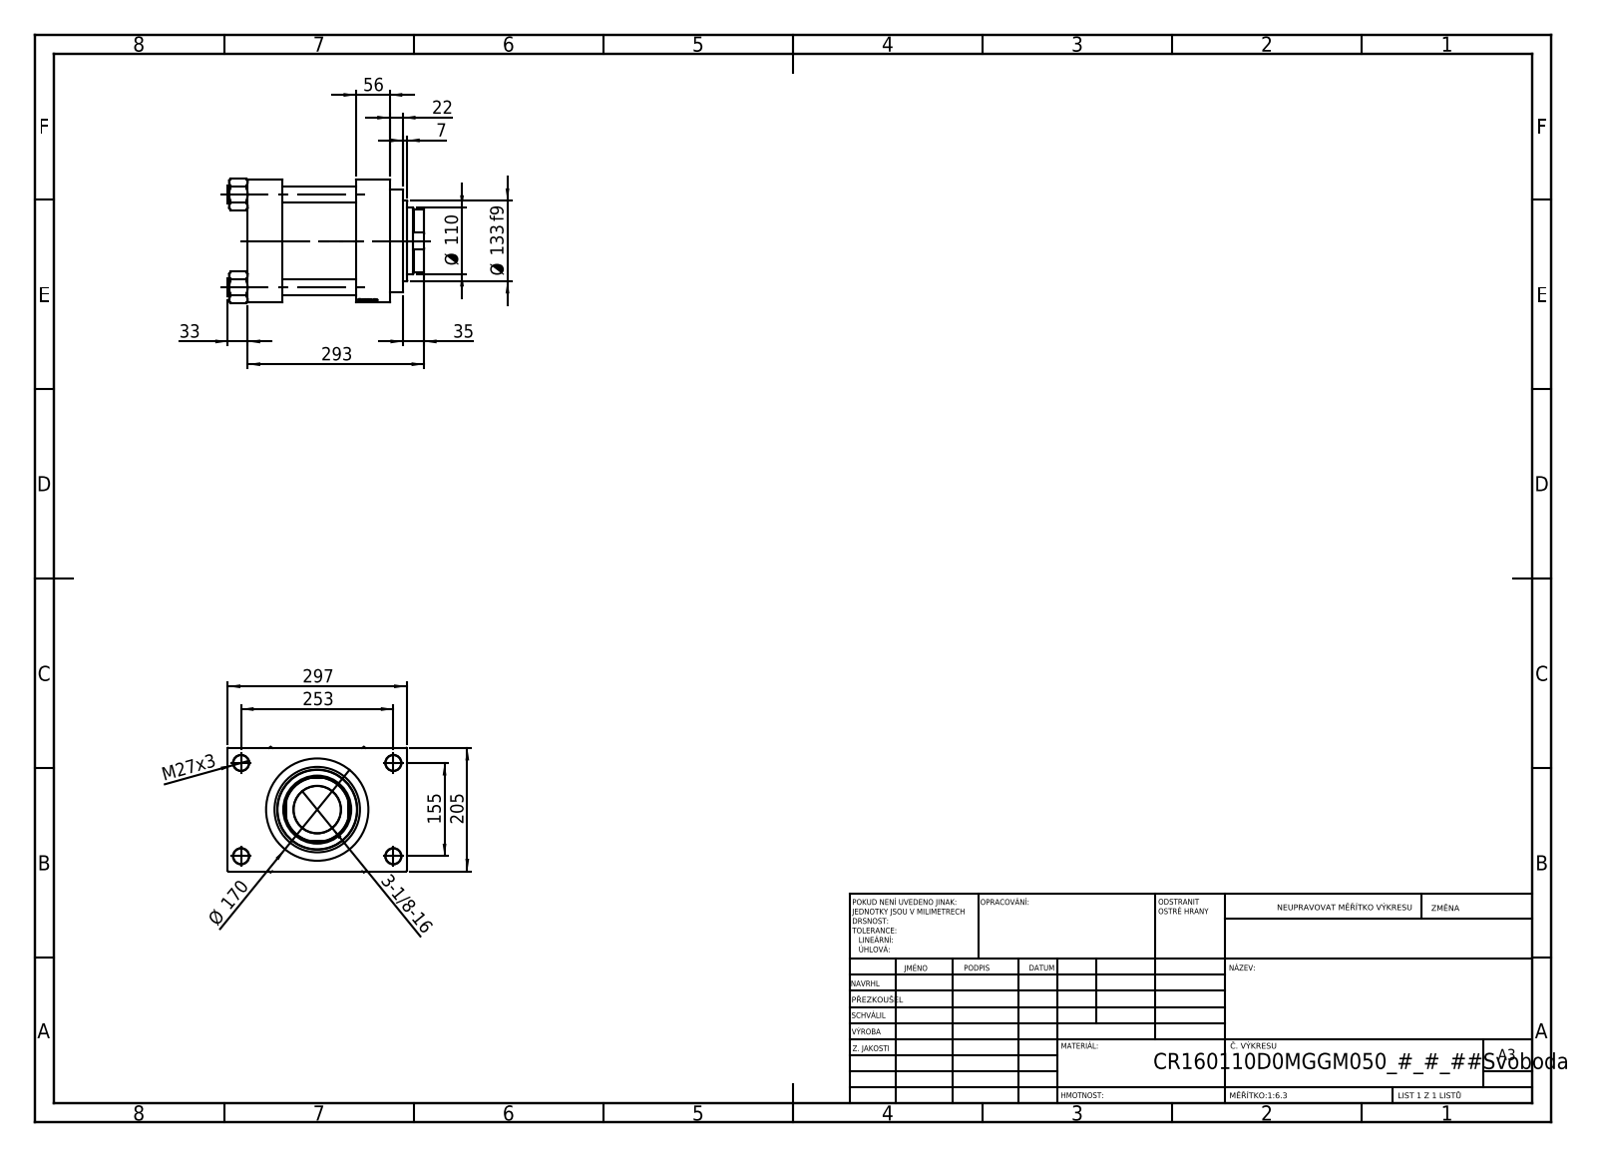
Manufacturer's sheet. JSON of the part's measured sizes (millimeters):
{"part_name": "V215CR_D_Body; NUT_M5_D; V215_VC_A; V215CR_D_TYCINKA (+1 more)", "step_written_by": "SolidWorks 2019 (CONFIG_CONTROL_DESIGN)", "units": "millimeters", "bodies": {"solids": 11, "faces": 1152, "planar": 545, "cylindrical": 89, "other": 518}, "overall_size": [326, 297, 208.14], "volume_mm3": 8567000, "surface_area_mm2": 825620, "round_holes": [[26, 4], [27, 4], [7, 2], [33.24, 2], [45, 2], [78.5, 1], [110, 1], [113, 1], [120, 1], [142, 1], [160, 1]], "round_bosses_or_shafts": [[30, 4], [170, 1], [166, 1], [133, 1]], "partial_cylinders_radius": [[54, 1]], "face_to_face_distances": [58, 180, 122, 205, 236, 178, 56, 46, 251, 72], "hole_center_spacings": [49.05, 109.53, 148.35, 154.9, 162.53, 203.95, 256.13, 155]}
